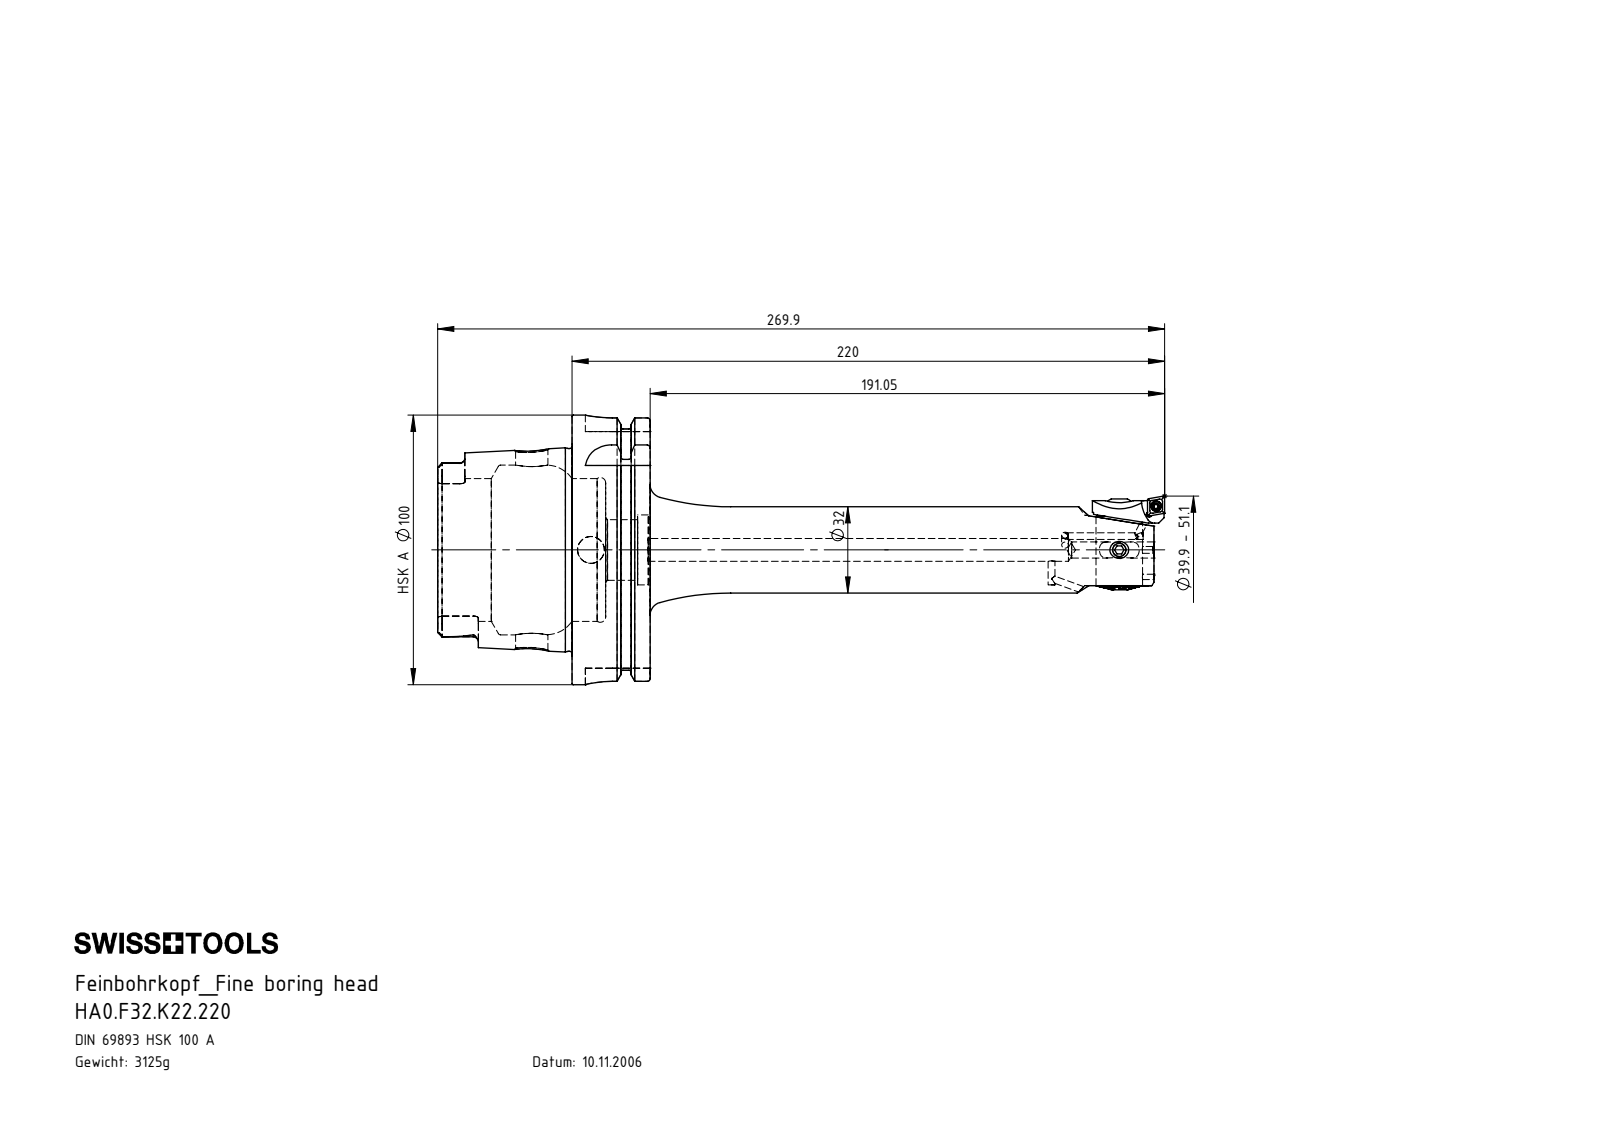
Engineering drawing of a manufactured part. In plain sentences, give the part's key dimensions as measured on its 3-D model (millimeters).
The part is named "F32-WCA.001.007; DIN 3771 - 15x1; F32; WCA-ER2.001.006_A (+8 more)". Its 3-D file was written by "SolidWorks 2022 (AUTOMOTIVE_DESIGN)". It is 12 solids with 833 faces: 336 planar, 171 cylindrical and 326 other. Overall it measures 269.9 by 100 by 100 millimeters. Its volume is 397 605 cubic millimeters and its surface area 80 525 square millimeters. Round holes: 5 of diameter 2.5, 2 of diameter 5, 2 of diameter 8.5, 1 of diameter 2, 1 of diameter 2.05, 1 of diameter 2.1, 1 of diameter 2.7, 1 of diameter 2.8, 1 of diameter 2.9, 1 of diameter 3, 1 of diameter 3.85, 1 of diameter 6. Round bosses or shafts: 2 of diameter 10, 1 of diameter 100, 1 of diameter 91.95, 1 of diameter 75.26, 1 of diameter 32, 1 of diameter 17, 1 of diameter 16.98, 1 of diameter 16.85. Partial cylindrical surfaces (rounded edges, fillets, slot ends): 7 of radius 1.9, 6 of radius 0.21, 5 of radius 10, 4 of radius 0.36, 4 of radius 0.5, 4 of radius 4.88, 2 of radius 0.36, 2 of radius 1.75. The main face-to-face distances are 28.95, 12.45, 16.5, 49.9, 62.35, 78.85, 15.85, 78.2, 28.3, 0.65. The hole center spacings are 3.84, 3.99, 5.6, 5.7, 8, 9.85, 10.61, 11.68.
